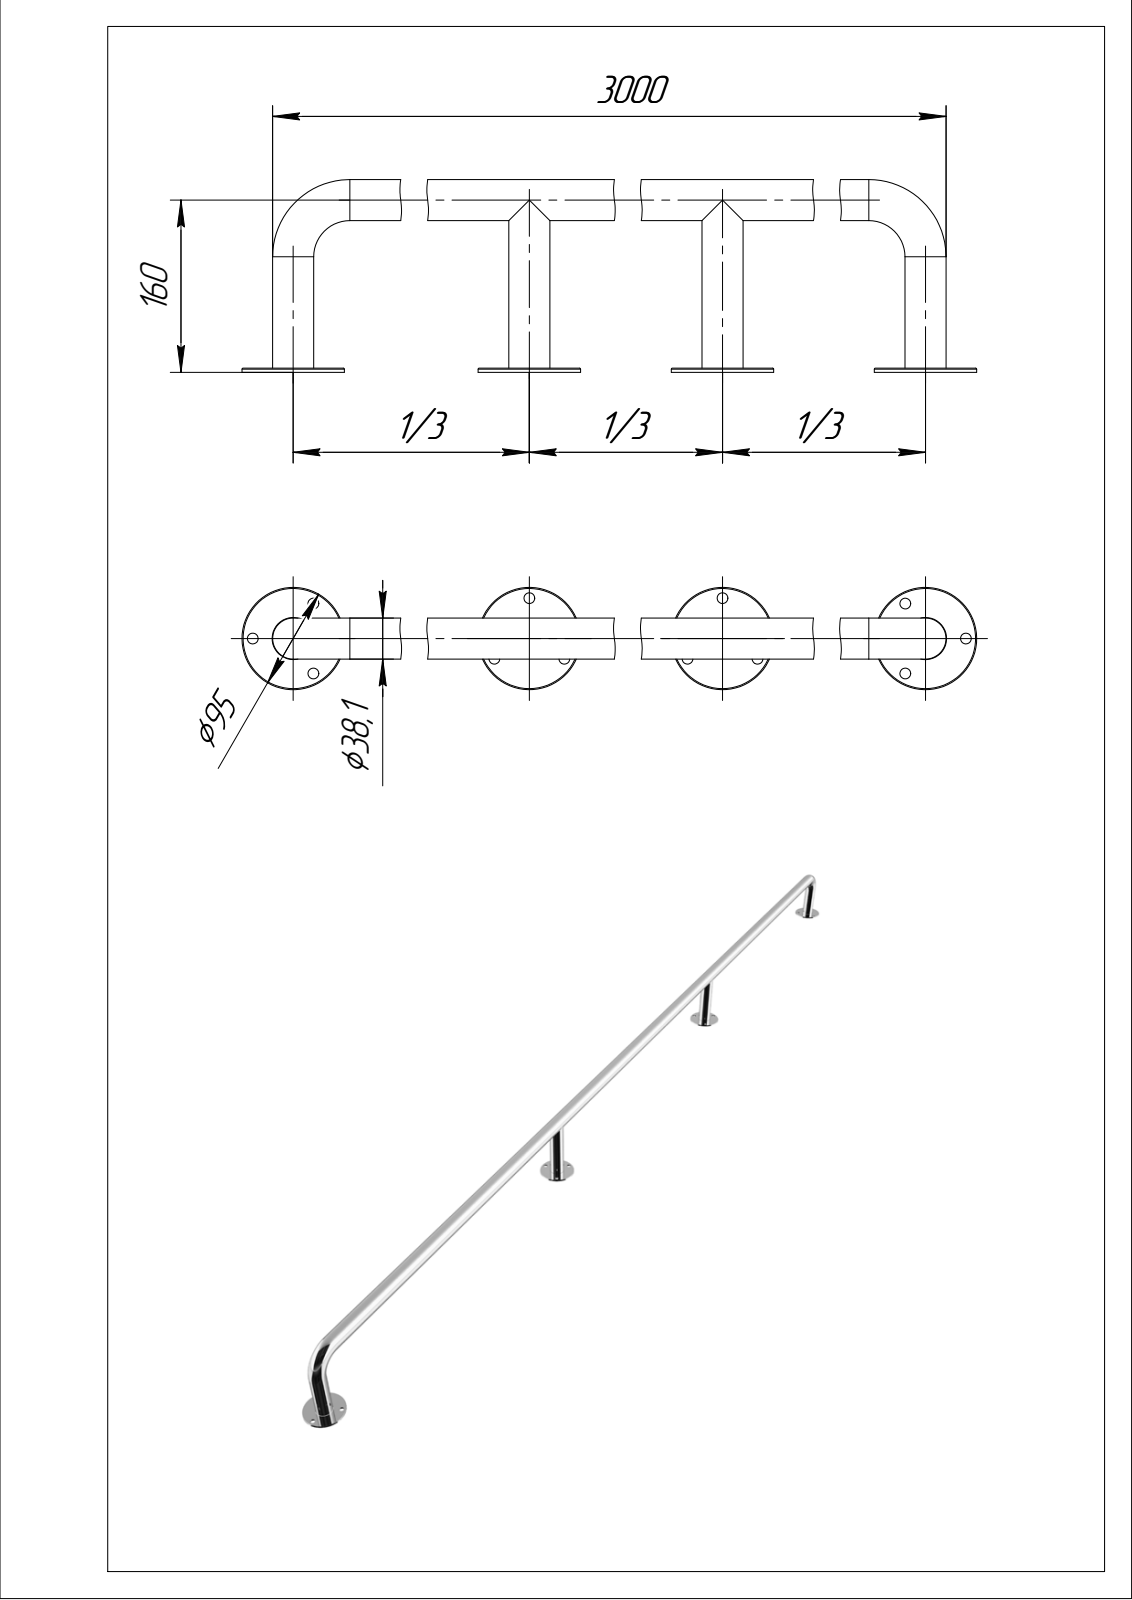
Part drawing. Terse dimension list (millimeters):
name: Сборка; Деталь; Фланец; Тр 2-38,1
written by: ASCON Math Kernel (AUTOMOTIVE_DESIGN)
unit: mm
bodies: 11 solids, 72 faces (20 planar, 38 cylindrical, 14 other)
size: 3056.9 × 179.05 × 95
volume: 550 580 mm³; area: 890 468 mm²
holes: 12× ⌀10, 3× ⌀36.1, 2× ⌀6, 2× ⌀35.1, 2× ⌀39.1, 1× ⌀38.1
bosses: 4× ⌀95, 4× ⌀38.1, 2× ⌀35
face distances: 4, 12, 8, 170, 166, 158
hole spacings: 37.5, 64.95, 987.3, 64.96, 955, 969.09, 988.01, 1019.95
